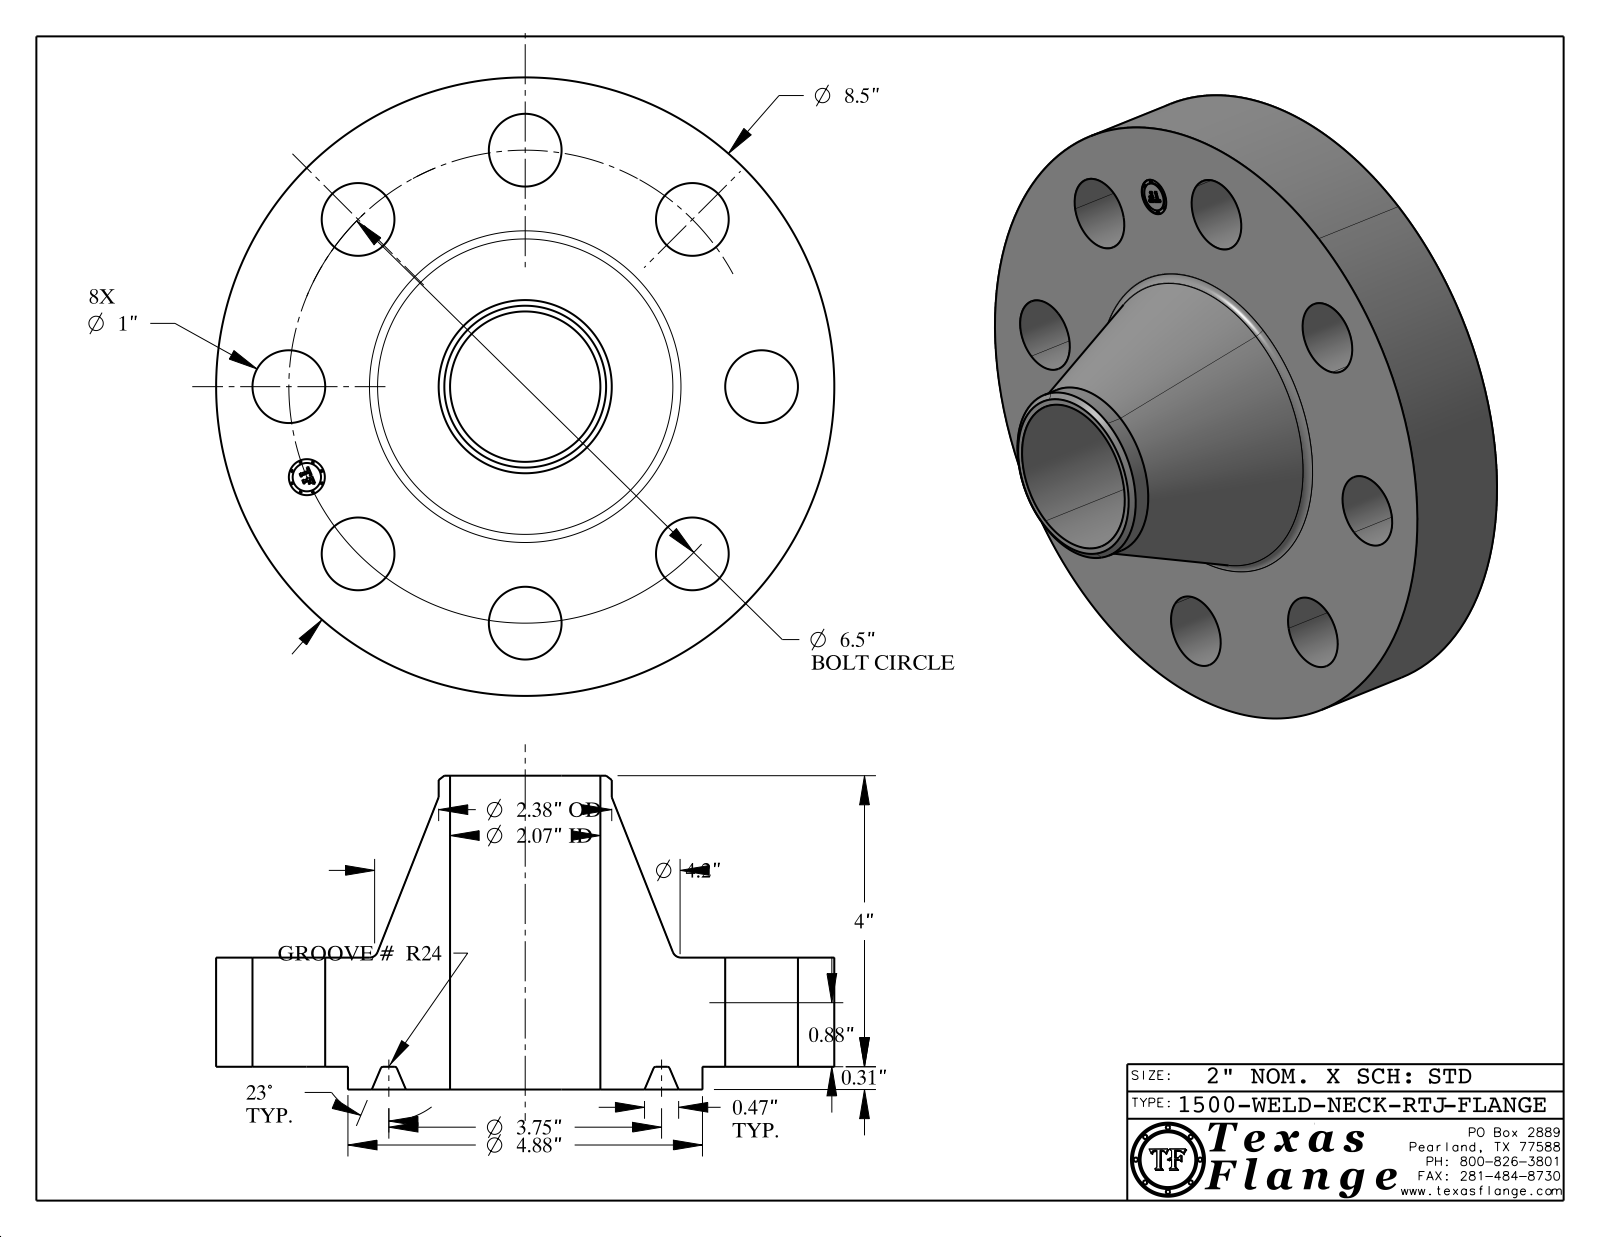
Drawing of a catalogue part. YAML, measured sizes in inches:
part_name: "1500-WELD-NECK-RTJ"
step_written_by: "CATIA V5 STEP AP214 (AUTOMOTIVE_DESIGN)"
units: inches
bodies: {solids: 1, faces: 429, planar: 371, cylindrical: 44, other: 14}
overall_size: [8.5, 8.5, 4.313]
volume: 85.86
surface_area: 226.6
round_holes:
  - {diameter: 1, count: 8}
  - {diameter: 0.495, count: 1}
  - {diameter: 2.067, count: 1}
round_bosses_or_shafts:
  - {diameter: 0.03, count: 8}
  - {diameter: 8.5, count: 1}
  - {diameter: 4.875, count: 1}
  - {diameter: 2.38, count: 1}
  - {diameter: 0.39, count: 1}
face_to_face_distances: [1.5, 0.313, 1.813, 4.313, 4, 2.5, 1.798, 1.485, 0.015, 2.515]
hole_center_spacings: [3.25, 2.487, 4.596, 6.005, 6.5, 1.268, 5.405, 6.375]
